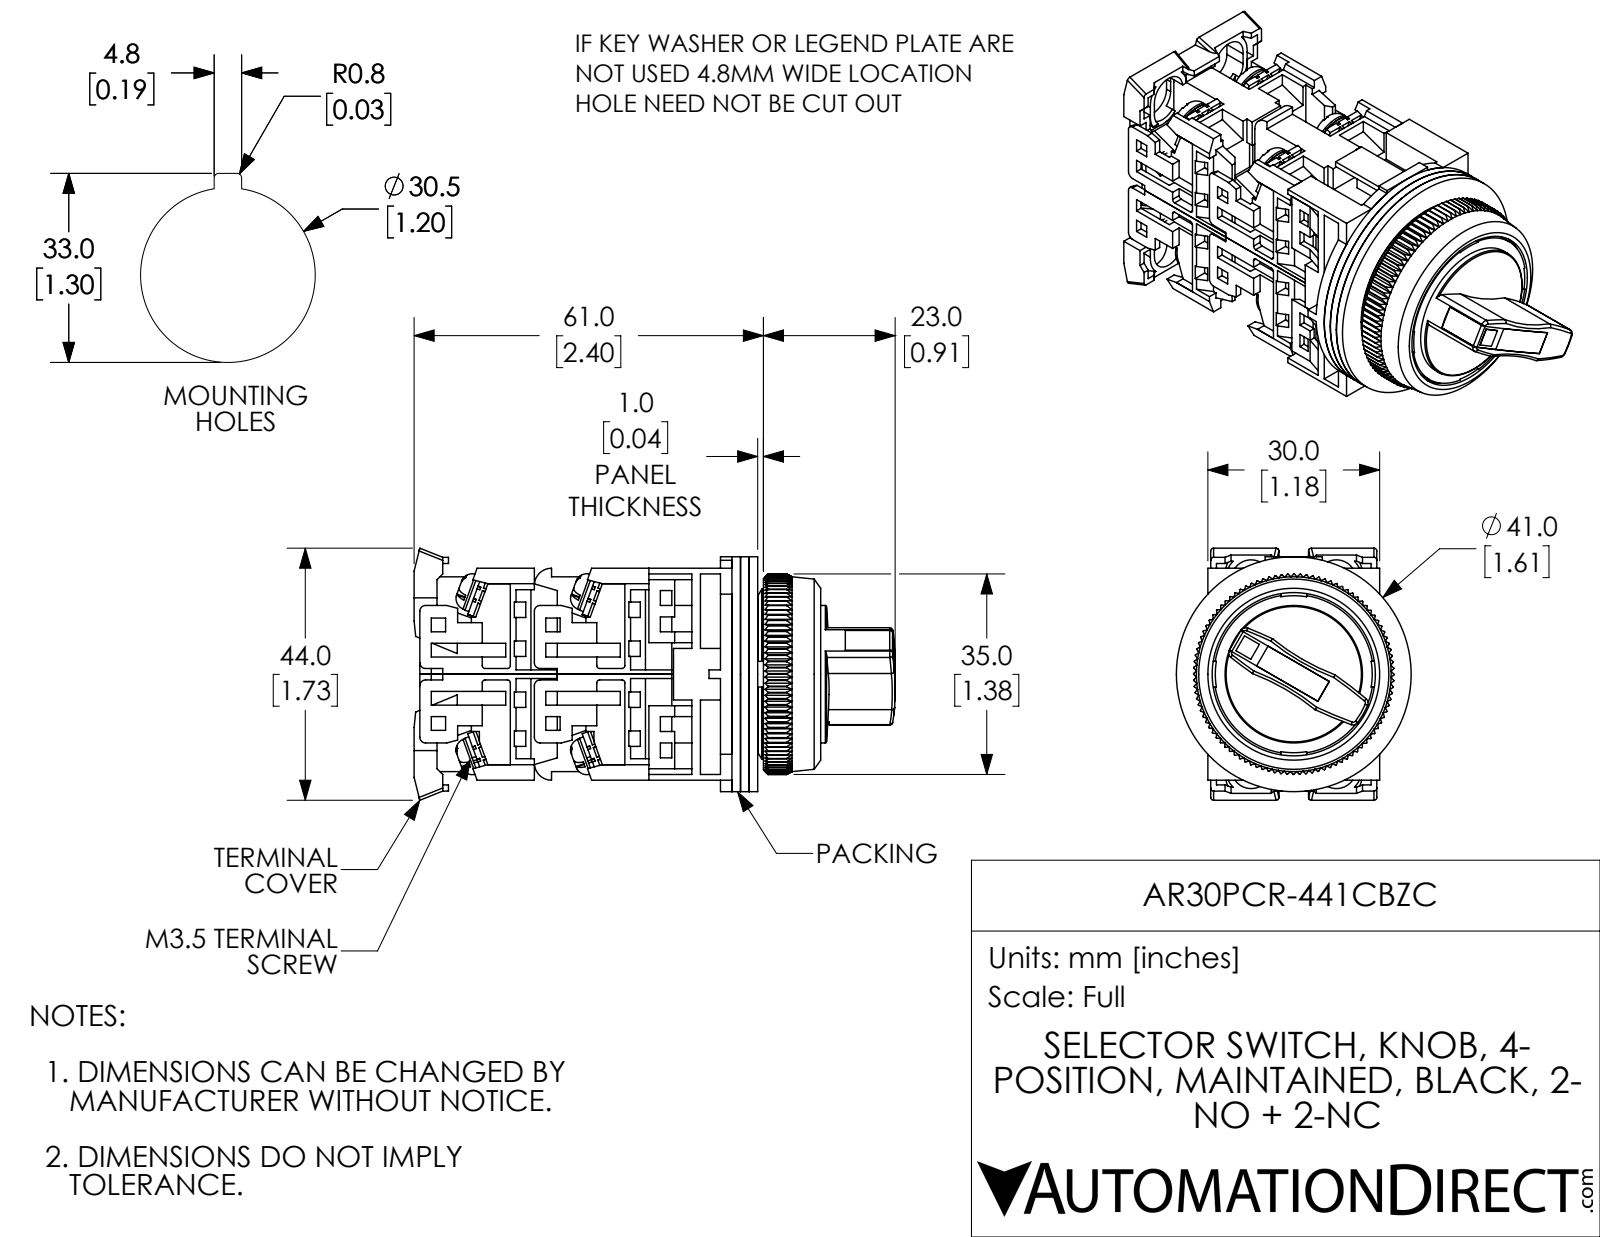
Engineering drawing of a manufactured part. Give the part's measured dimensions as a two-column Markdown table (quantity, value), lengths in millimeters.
| quantity | value |
| --- | --- |
| part name | AR30PCR-441CBZC |
| STEP written by | SolidWorks 2017 (AUTOMOTIVE_DESIGN) |
| units | millimeters |
| bodies | 39 solids, 2466 faces (1837 planar, 386 cylindrical, 243 other) |
| overall size | 84 × 44 × 41 |
| volume | 51 600 mm³ |
| surface area | 48 290 mm² |
| round holes (diameter × count) | 3.5 × 16, 3.6 × 8, 3 × 1, 8 × 1, 12 × 1, 12.2 × 1, 13 × 1, 20.8 × 1, 24 × 1, 28.5 × 1, 31.8 × 1 |
| round bosses / shafts (diameter × count) | 6.6 × 8, 3.5 × 8, 41 × 1, 30 × 1, 20 × 1, 18 × 1, 17 × 1, 14.2 × 1 |
| partial cylindrical surfaces (radius × count) | 1.5 × 32, 0.5 × 17, 1 × 12, 3 × 4, 3.5 × 4, 4.5 × 4, 40 × 2, 41.6 × 2 |
| main face-to-face distances | 1.5, 1, 3, 1.6, 20, 0.5, 17.5, 2.3, 1.7, 0.7 |
| hole center spacings | 14.7, 16.2, 6.8, 6.8, 15.5 |
